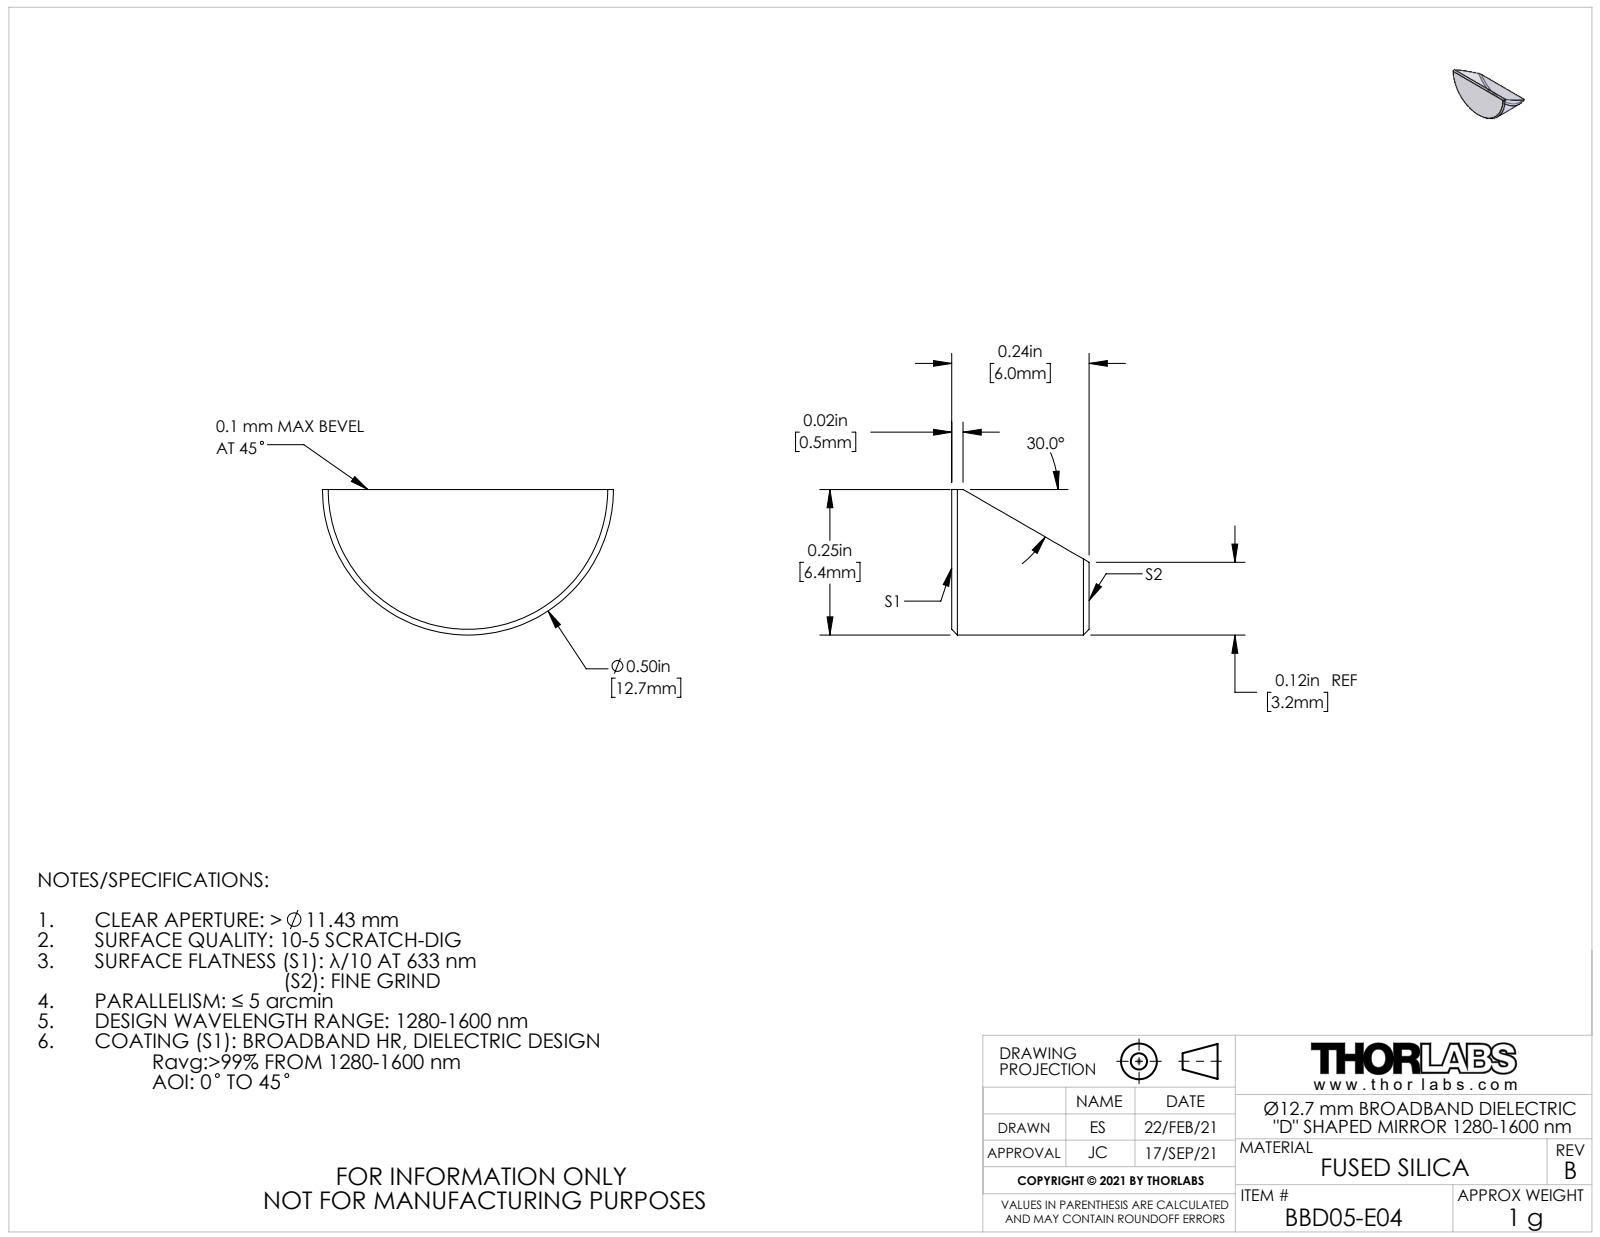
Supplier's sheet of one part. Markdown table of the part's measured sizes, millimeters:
| quantity | value |
| --- | --- |
| part name | TTN227581-E0W |
| STEP written by | SolidWorks 2018 (CONFIG_CONTROL_DESIGN) |
| units | millimeters |
| bodies | 1 solid, 7 faces (4 planar, 1 cylindrical, 2 other) |
| overall size | 12.7 × 6.35 × 6 |
| volume | 270 mm³ |
| surface area | 268 mm² |
| partial cylindrical surfaces (radius × count) | 6.35 × 1 |
| main face-to-face distances | 6 |
